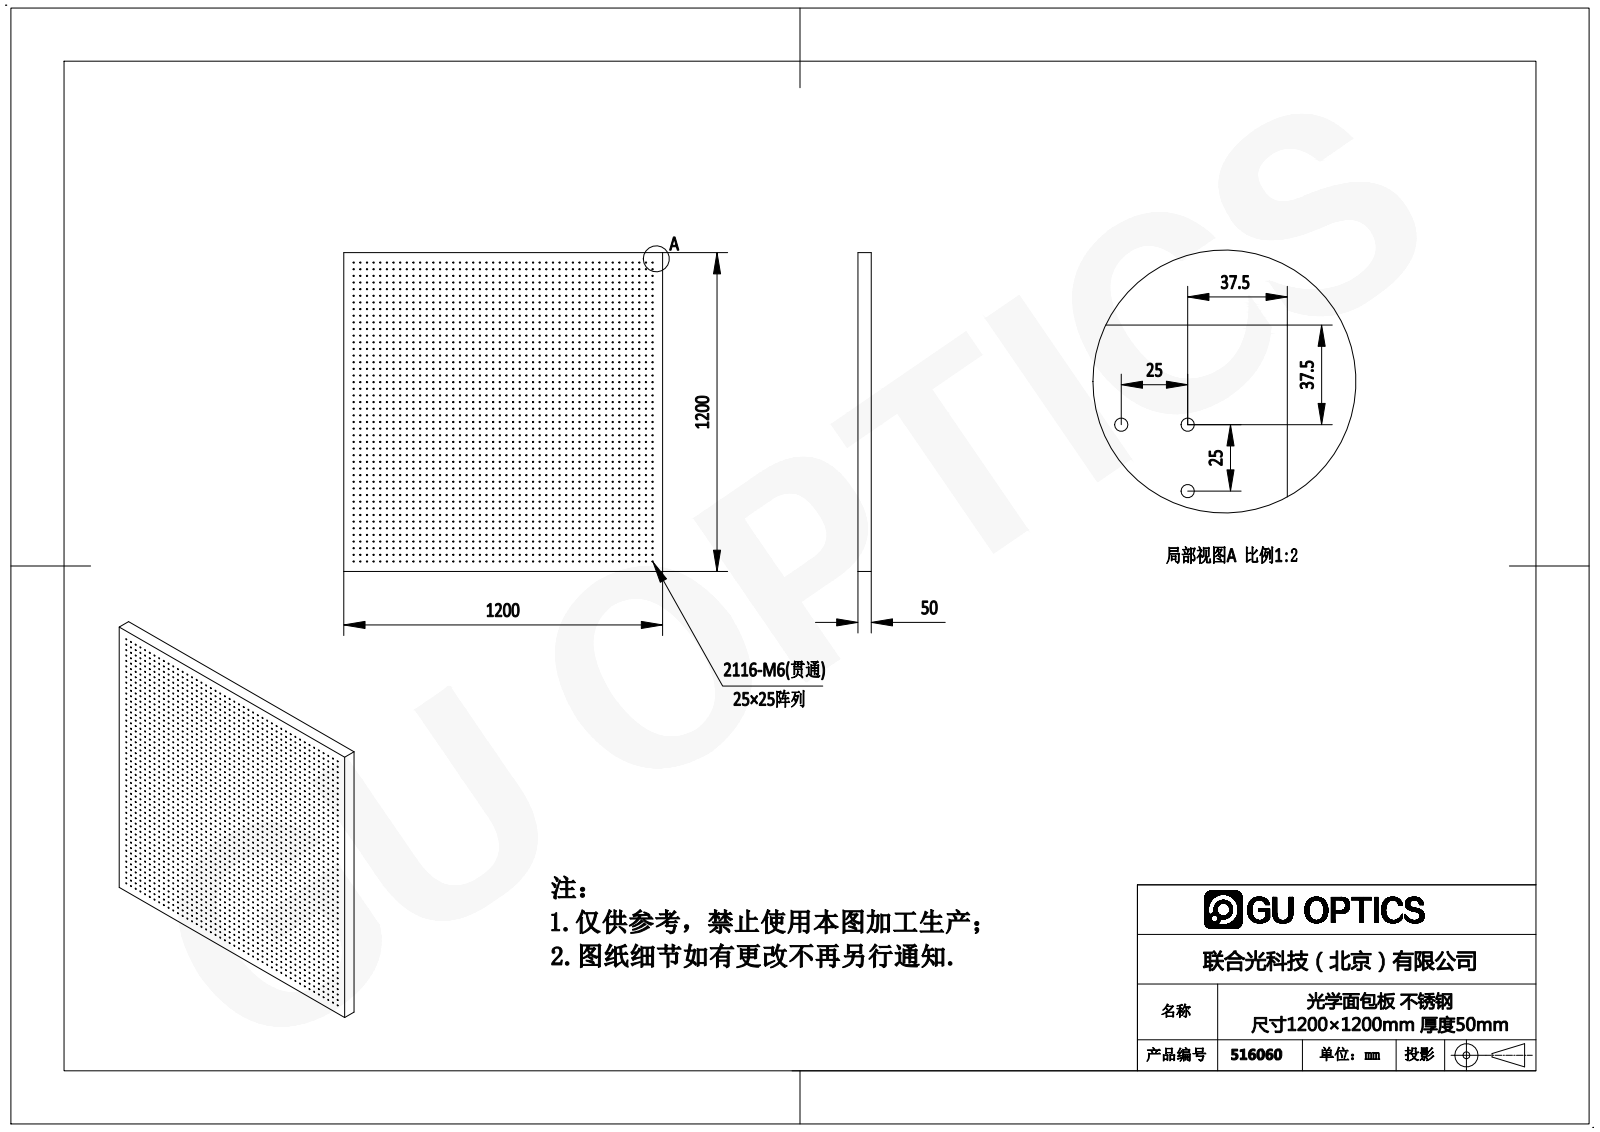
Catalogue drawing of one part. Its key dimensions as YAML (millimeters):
part_name: "516060"
step_written_by: "SolidWorks 2016 (AUTOMOTIVE_DESIGN)"
units: millimeters
bodies: {solids: 1, faces: 4238, planar: 6, cylindrical: 4232, other: 0}
overall_size: [1200, 1200, 50]
volume: 69920000
surface_area: 4699000
round_holes:
  - {diameter: 5, count: 2116}
face_to_face_distances: [50, 1200]
hole_center_spacings: [25, 50, 75, 100, 125, 150, 175, 200]
